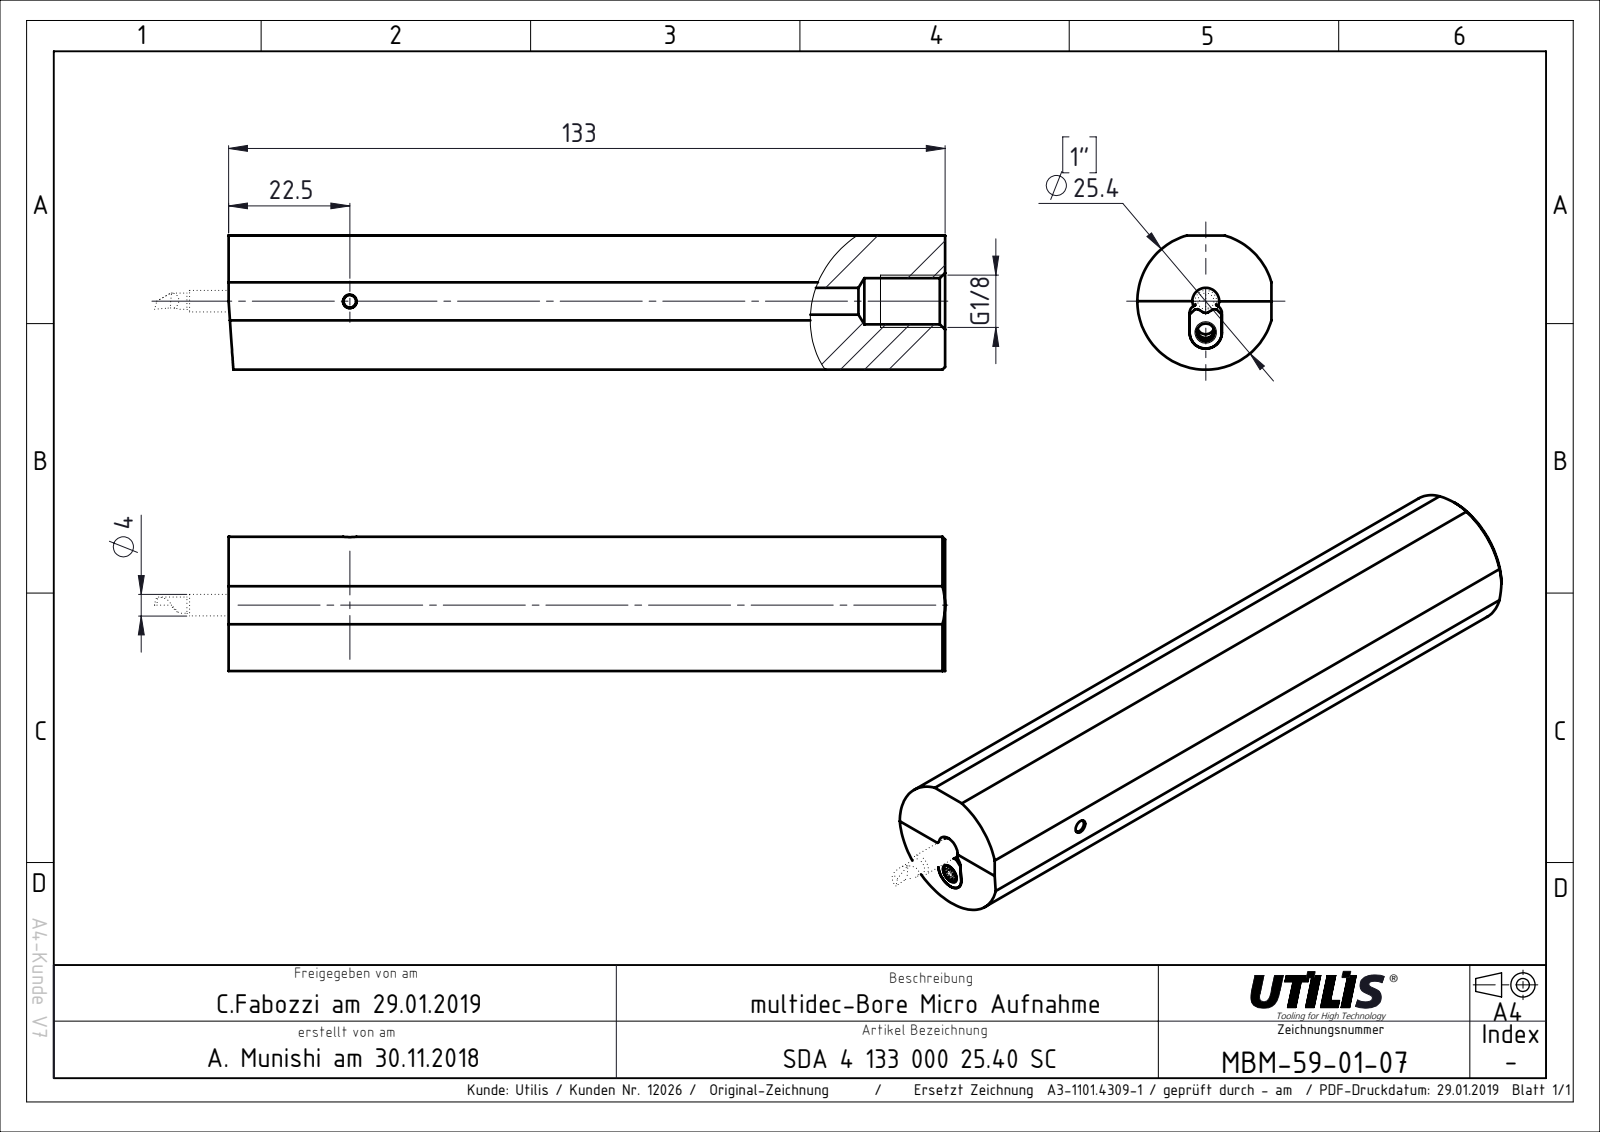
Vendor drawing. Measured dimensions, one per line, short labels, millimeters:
name: UTP AblageMBM-59-01-01-07
written by: SolidWorks 2018 (CONFIG_CONTROL_DESIGN)
unit: mm
bodies: 1 solid, 41 faces (8 planar, 17 cylindrical, 16 other)
size: 133 × 24.9 × 24.9
volume: 63 065 mm³; area: 14 059 mm²
holes: 1× ⌀2.5, 1× ⌀3.3, 1× ⌀4, 1× ⌀5, 1× ⌀8.57
bosses: 1× ⌀25.4
rounds: 1× R3
face distances: 133, 9.2, 6, 15.2, 8.8
